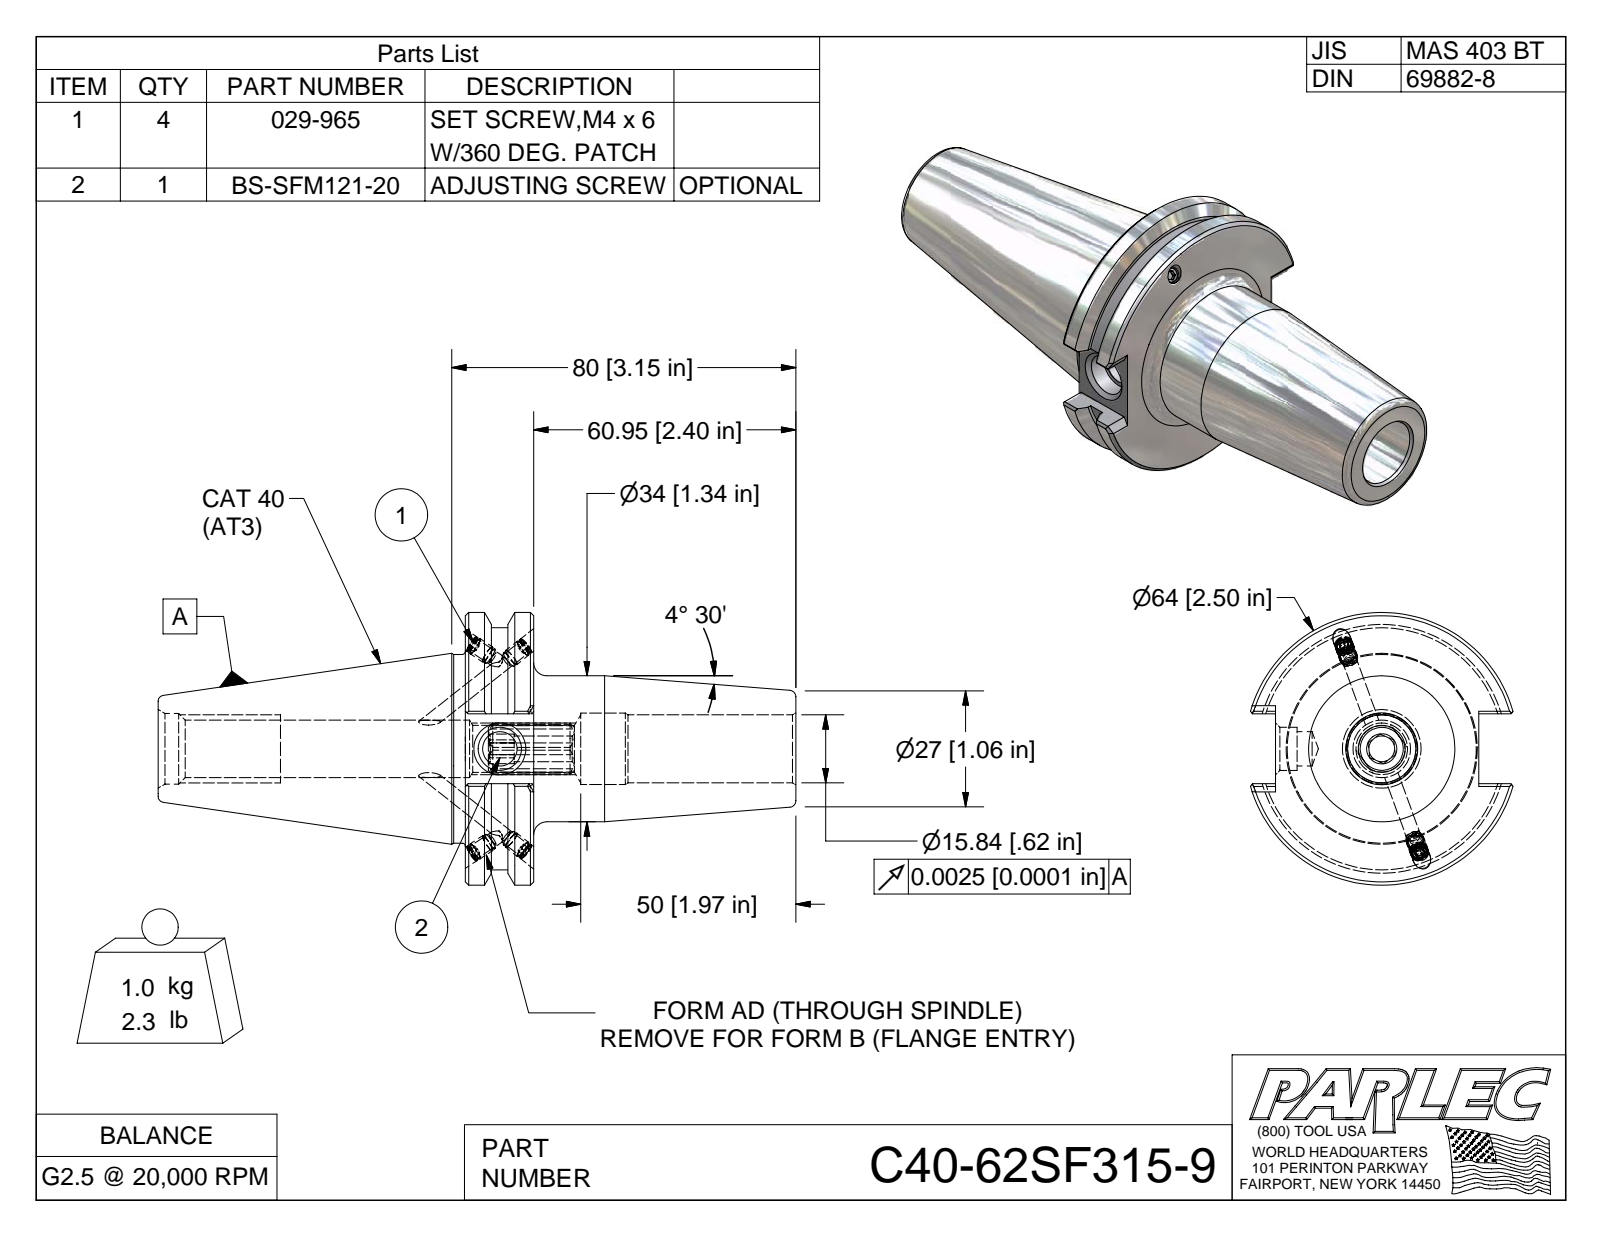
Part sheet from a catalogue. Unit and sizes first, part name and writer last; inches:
Units: inches
Overall size (bounding box): 5.837 × 2.5 × 2.403
Round holes (diameter × count): ⌀0.13 ×4, ⌀0.161 ×4, ⌀0.624 ×1, ⌀0.654 ×1
Round bosses / shafts (diameter × count): ⌀0.165 ×4, ⌀0.157 ×4, ⌀2.5 ×1, ⌀2.219 ×1, ⌀1.73 ×1, ⌀1.339 ×1
Partial cylindrical surfaces — rounded edges, fillets, slot ends (radius × count): R0.236 ×1
Main face-to-face distances: 0.625, 3.025, 2.4, 0.64, 0.236, 1.86, 0.394, 2.812, 3.437, 5.837
Volume: 8.461 in³ · Surface area: 48.02 in²
Bodies: 6 solids, 172 faces (87 planar, 32 cylindrical, 53 other)
Part name (STEP PRODUCT): C40-62SF315-9; C40BC-62SF315-9-1; 029-965; BS-SFM121-20
STEP written by: Autodesk Inventor 2009 (AUTOMOTIVE_DESIGN)
